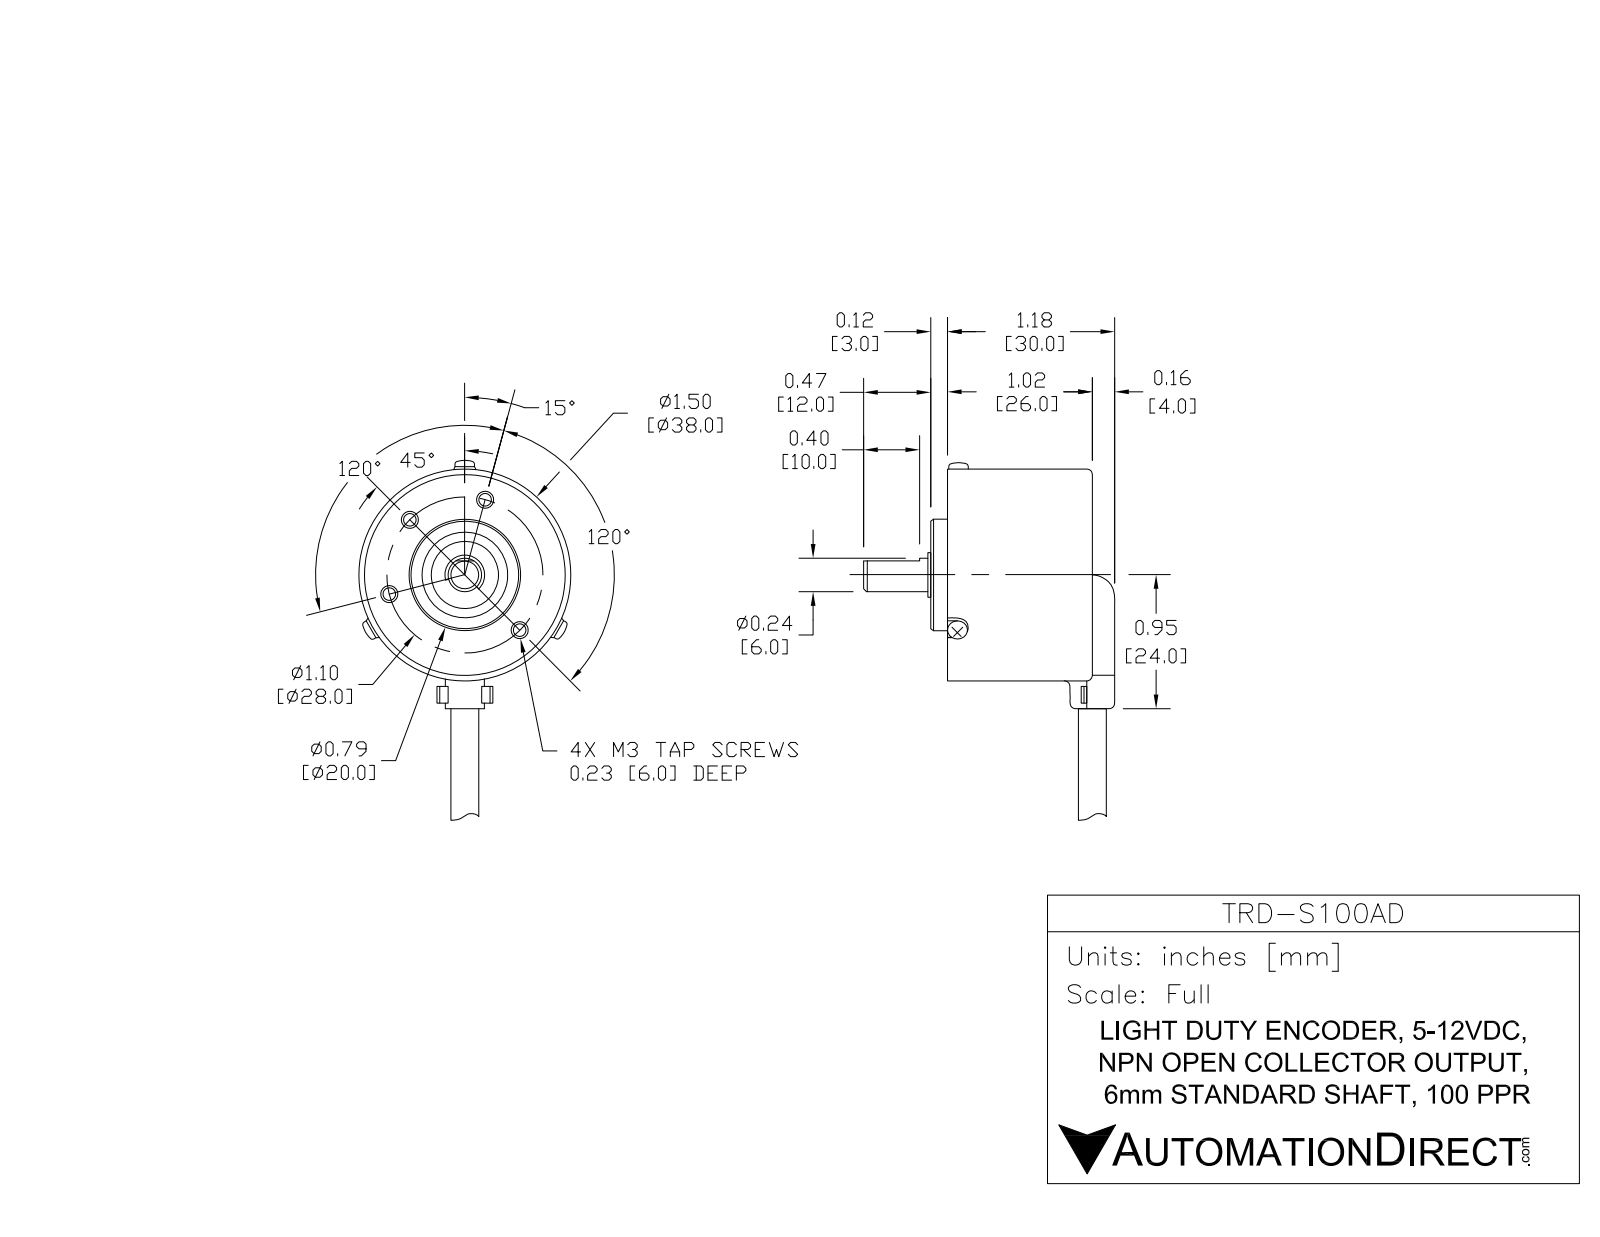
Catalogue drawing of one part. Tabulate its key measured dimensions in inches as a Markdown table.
| quantity | value |
| --- | --- |
| part name | TRD-S100AD |
| STEP written by | SolidWorks 2016 (AUTOMOTIVE_DESIGN) |
| units | inches |
| bodies | 3 solids, 257 faces (98 planar, 100 cylindrical, 59 other) |
| overall size | 7.189 × 1.768 × 1.496 |
| volume | 2.068 in³ |
| surface area | 13.85 in² |
| round holes (diameter × count) | 0.118 × 4, 0.205 × 1, 0.256 × 1, 1.409 × 1 |
| round bosses / shafts (diameter × count) | 1.496 × 1, 0.787 × 1, 0.591 × 1, 0.315 × 1, 0.236 × 1, 0.197 × 1, 0.193 × 1 |
| partial cylindrical surfaces (radius × count) | 0.016 × 11, 0.004 × 4, 0.13 × 3, 0.748 × 3, 0.008 × 2, 0.02 × 2, 0.146 × 2, 0.11 × 1 |
| main face-to-face distances | 1.024, 0.118, 1.142, 0.02, 0.138, 0.803, 1.161, 0.354, 0.335, 0.217 |
| hole center spacings | 0.551, 0.955, 0.954, 1.102 |
